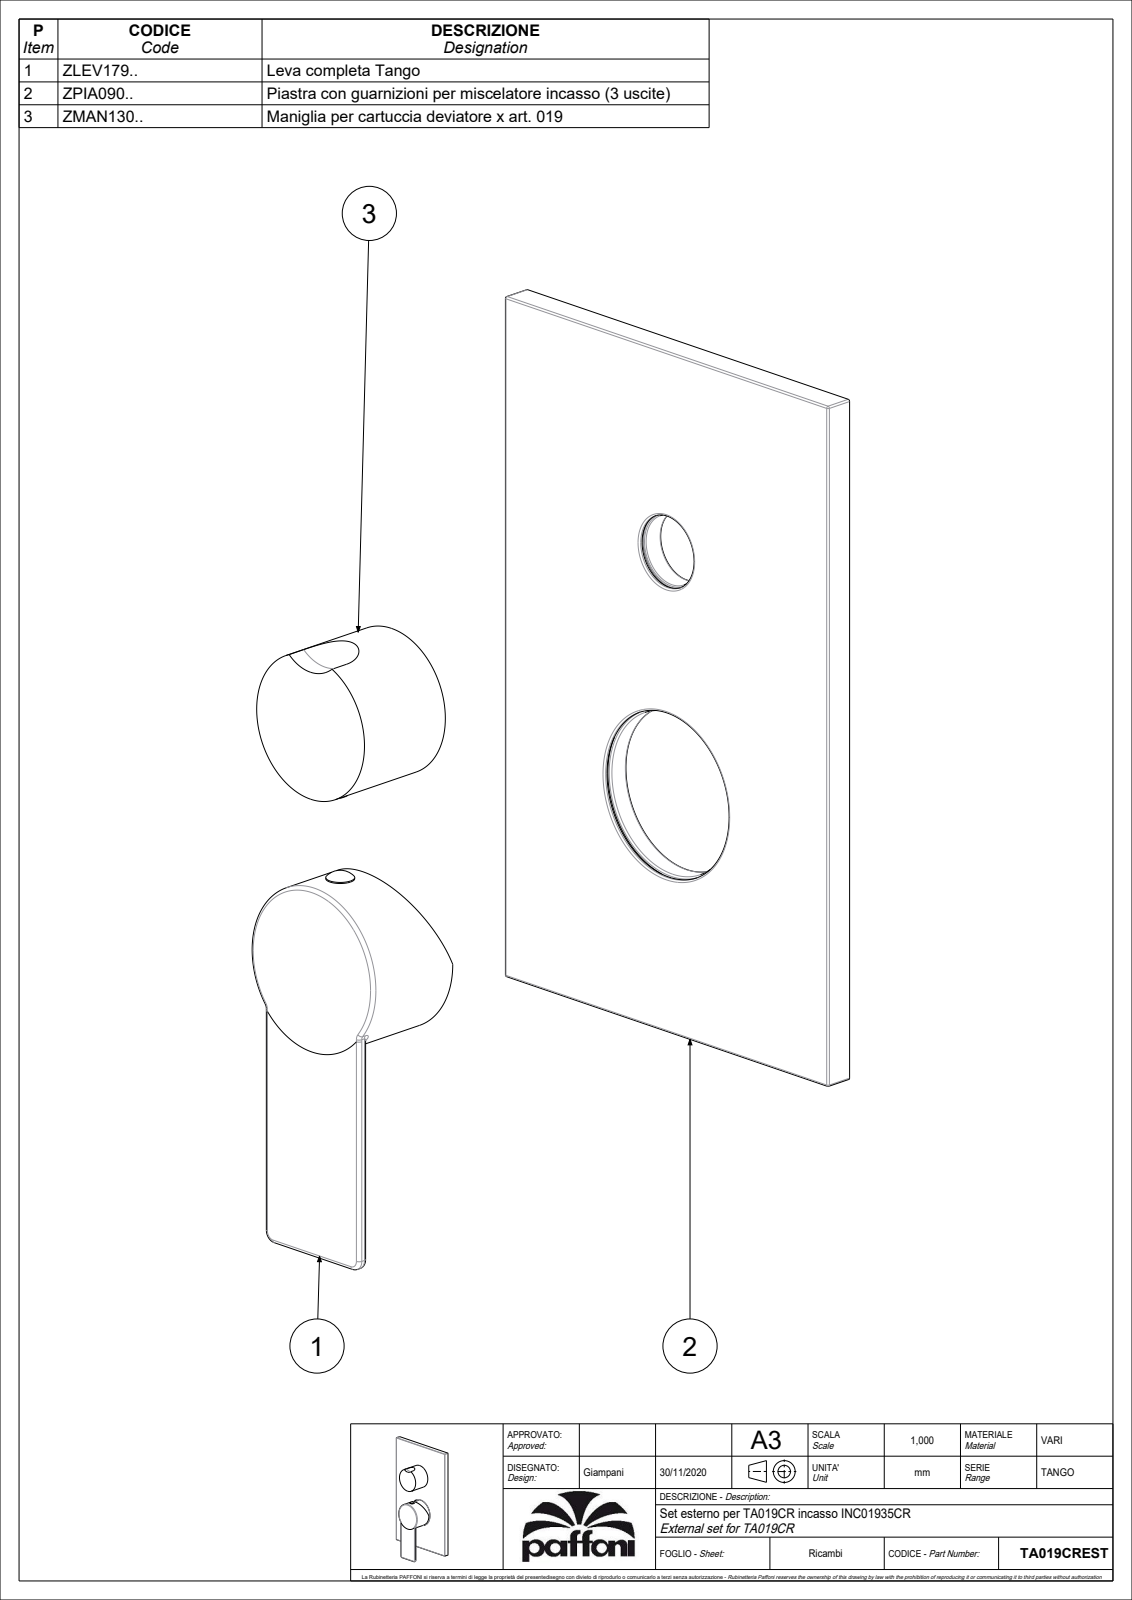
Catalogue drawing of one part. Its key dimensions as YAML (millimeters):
part_name: "TA019CREST"
step_written_by: "CREO PARAMETRIC BY PTC INC, 2020044 (CONFIG_CONTROL_DESIGN)"
units: millimeters
bodies: {solids: 3, faces: 279, planar: 99, cylindrical: 96, other: 84}
overall_size: [204, 120, 40.35]
volume: 158078
surface_area: 101555
round_holes:
  - {diameter: 3, count: 2}
  - {diameter: 3.2, count: 1}
  - {diameter: 4.2, count: 1}
  - {diameter: 14.8, count: 1}
  - {diameter: 19.2, count: 1}
  - {diameter: 20, count: 1}
  - {diameter: 21, count: 1}
  - {diameter: 23.2, count: 1}
  - {diameter: 36, count: 1}
  - {diameter: 45, count: 1}
  - {diameter: 46, count: 1}
  - {diameter: 47, count: 1}
round_bosses_or_shafts:
  - {diameter: 7.6, count: 2}
  - {diameter: 5.5, count: 2}
  - {diameter: 51, count: 1}
  - {diameter: 49, count: 1}
  - {diameter: 45.5, count: 1}
  - {diameter: 40, count: 1}
  - {diameter: 25, count: 1}
  - {diameter: 24, count: 1}
partial_cylinders:
  - {radius: 1, count: 14}
  - {radius: 0.5, count: 10}
  - {radius: 1.5, count: 4}
  - {radius: 3, count: 2}
  - {radius: 3.5, count: 1}
  - {radius: 12.5, count: 1}
face_to_face_distances: [2.5, 0.5, 3, 8, 5.5, 5, 31.5, 31, 22.5, 34.5]
hole_center_spacings: [1, 10, 68, 78]
